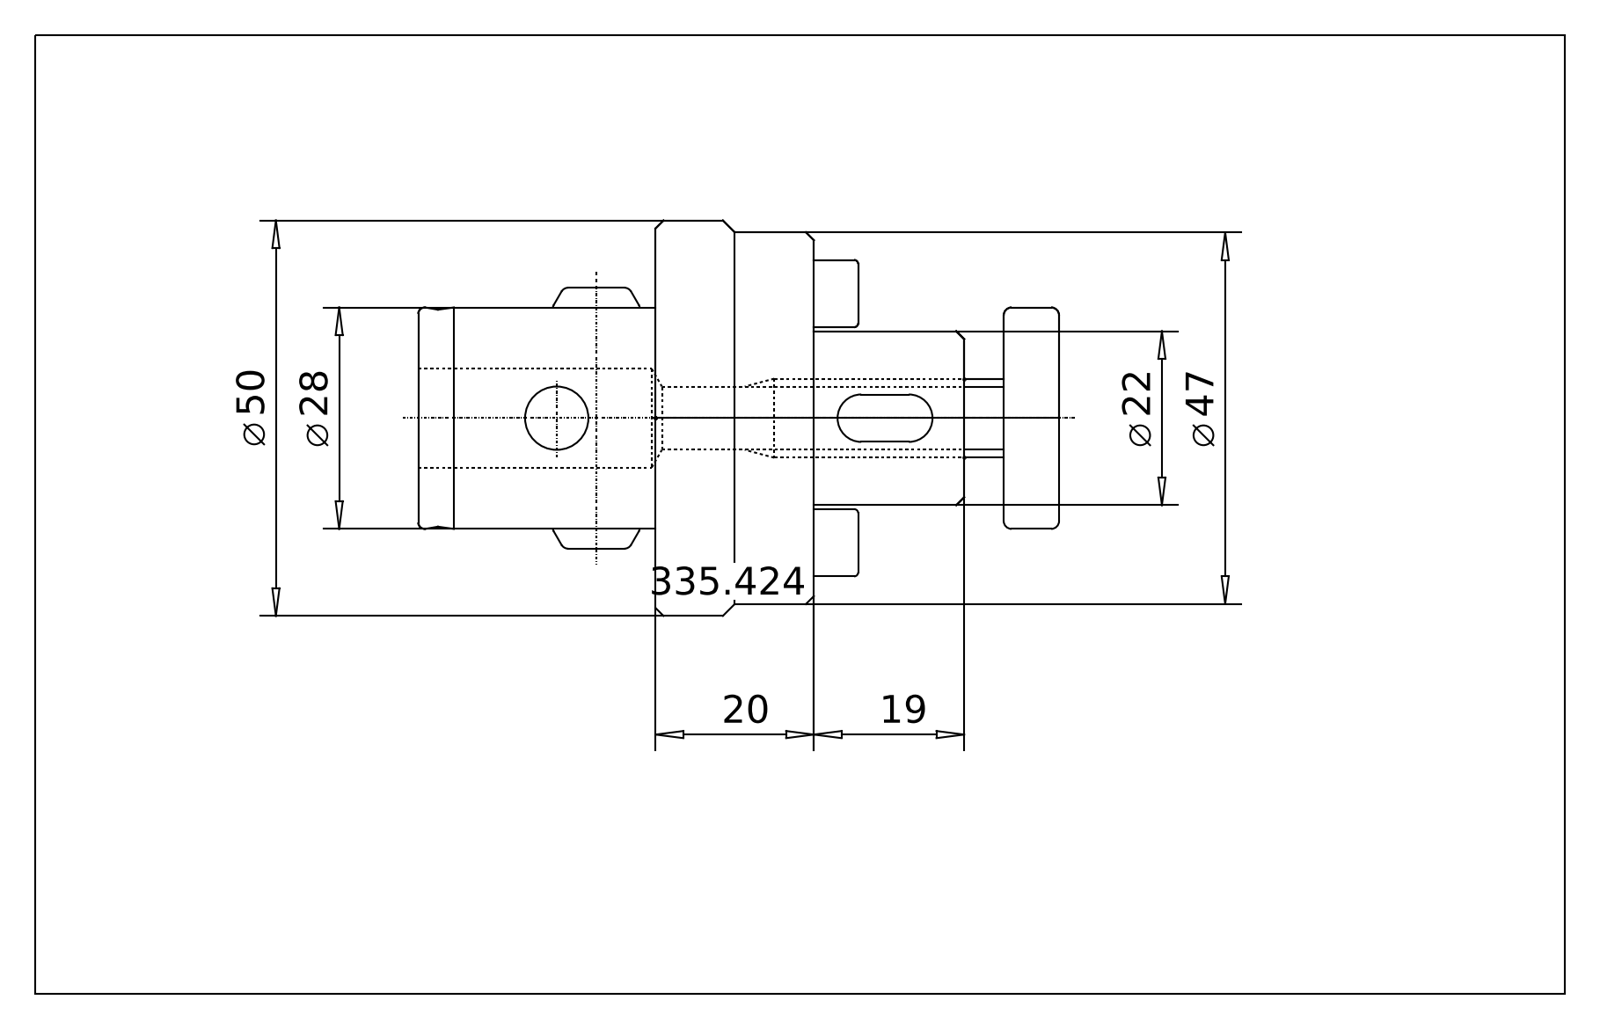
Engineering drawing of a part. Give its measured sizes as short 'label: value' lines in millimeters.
name: 335.424 Kaiser CKS5 X F22|691.606 Kaiser ETL MST 22 (Paar)_Standard;NONE; 335.424 Kaiser CKS5 X F22|691.601 Kaiser ETL FK 6 X 6_Standard;NONE; 335.424 Kaiser CKS5 X F22|690.704 Kaiser ETL FR22_M10_Standard-1;NONE; 335.424 Kaiser CKS5 X F22|690.704 Kaiser ETL FR22_M10_Standard;NONE (+3 more)
written by: ACIS (automotive_design)
unit: mm
bodies: 8 solids, 223 faces (69 planar, 78 cylindrical, 76 other)
size: 79.67 × 50 × 50
volume: 61 903 mm³; area: 21 059 mm²
holes: 2× ⌀3, 1× ⌀3.3, 1× ⌀4.3, 1× ⌀7.4, 1× ⌀8, 1× ⌀8.5, 1× ⌀10, 1× ⌀10.5, 1× ⌀12.5, 1× ⌀14.5, 1× ⌀16
bosses: 1× ⌀50, 1× ⌀47, 1× ⌀28, 1× ⌀22, 1× ⌀11, 1× ⌀7
rounds: 2× R3, 1× R5
face distances: 20, 8, 21.67, 41.67, 29.67, 49.67, 10, 79.67, 71.67, 50
